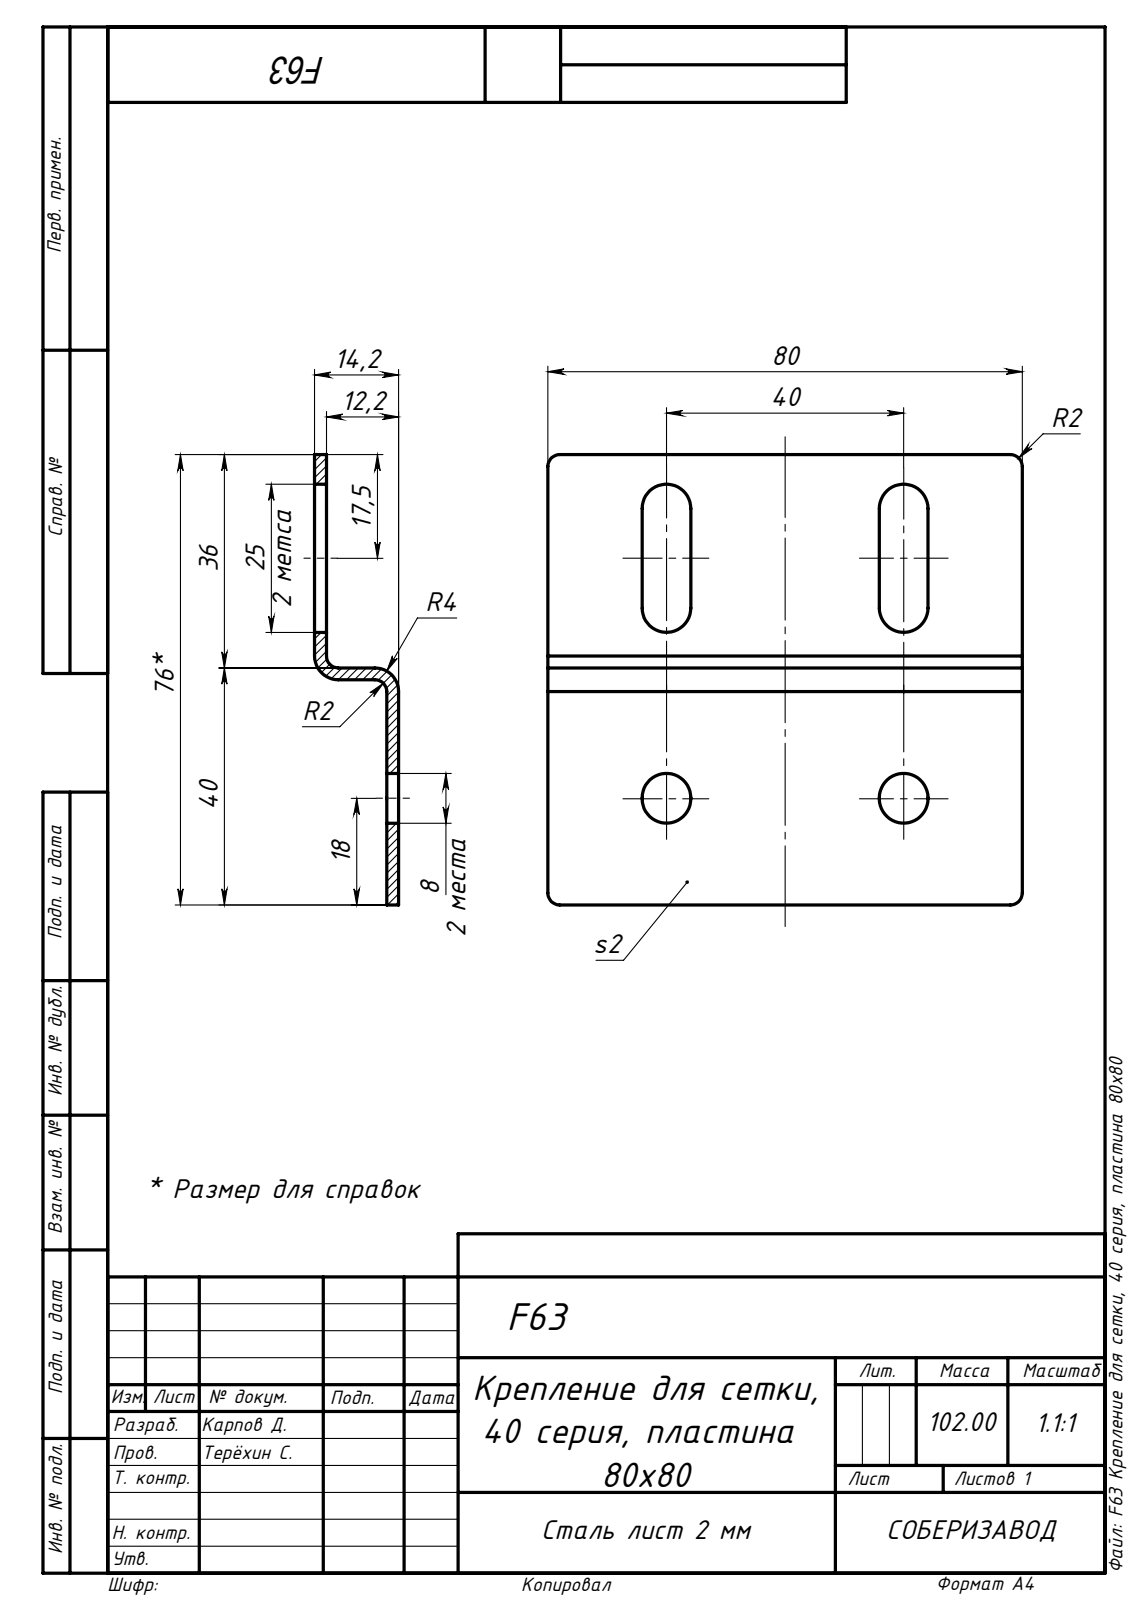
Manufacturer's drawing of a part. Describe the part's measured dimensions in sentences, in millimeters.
The part is named "F63 Крепление для сетки, 40 серия, пластина 80х80". Its 3-D file was written by "SolidWorks 2020 (AUTOMOTIVE_DESIGN)". It is 1 solid with 46 faces: 26 planar, 20 cylindrical and 0 other. Overall it measures 80 by 76 by 14.17 millimeters. Its volume is 12 708 cubic millimeters and its surface area 13 706 square millimeters. Partial cylindrical surfaces (rounded edges, fillets, slot ends): 8 of radius 4.1, 6 of radius 2, 2 of radius 4. The main face-to-face distances are 2, 12.17, 14.17, 10.17, 38, 40, 80, 76, 36, 15.9.
